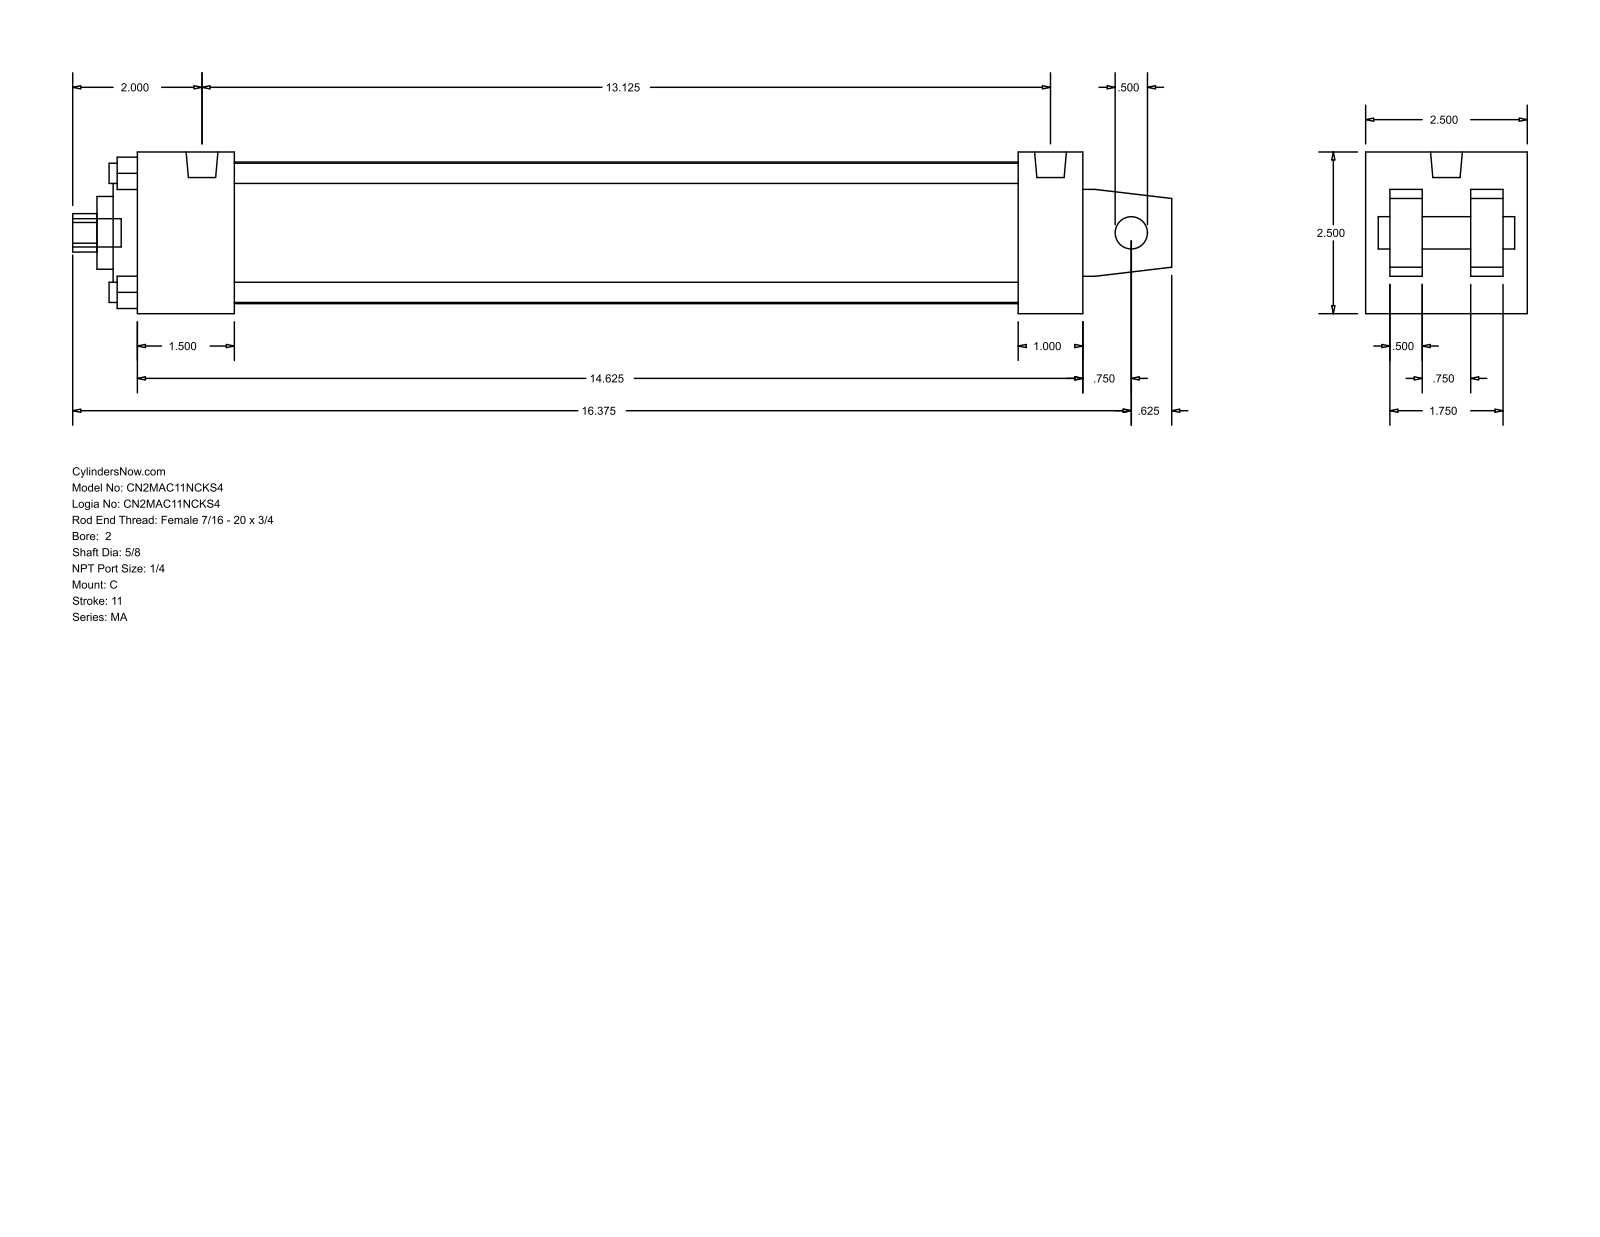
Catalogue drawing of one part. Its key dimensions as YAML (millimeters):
part_name: "MA_C__0200_0.625"
step_written_by: "GSSL Pune (CONFIG_CONTROL_DESIGN)"
units: millimeters
bodies: {solids: 0, faces: 105, planar: 77, cylindrical: 28, other: 0}
overall_size: [431.8, 63.5, 63.5]
round_holes:
  - {diameter: 7.94, count: 4}
  - {diameter: 12.7, count: 1}
  - {diameter: 15.88, count: 1}
  - {diameter: 28.57, count: 1}
  - {diameter: 50.8, count: 1}
  - {diameter: 55.63, count: 1}
round_bosses_or_shafts:
  - {diameter: 7.94, count: 4}
  - {diameter: 12.49, count: 2}
  - {diameter: 11.11, count: 1}
partial_cylinders:
  - {radius: 7.54, count: 1}
face_to_face_distances: [63.5, 9.52, 12.7, 22.22, 41.28, 53.98, 31.76, 25.4, 38.1, 371.48]
hole_center_spacings: [33.05, 46.74, 66.1]
